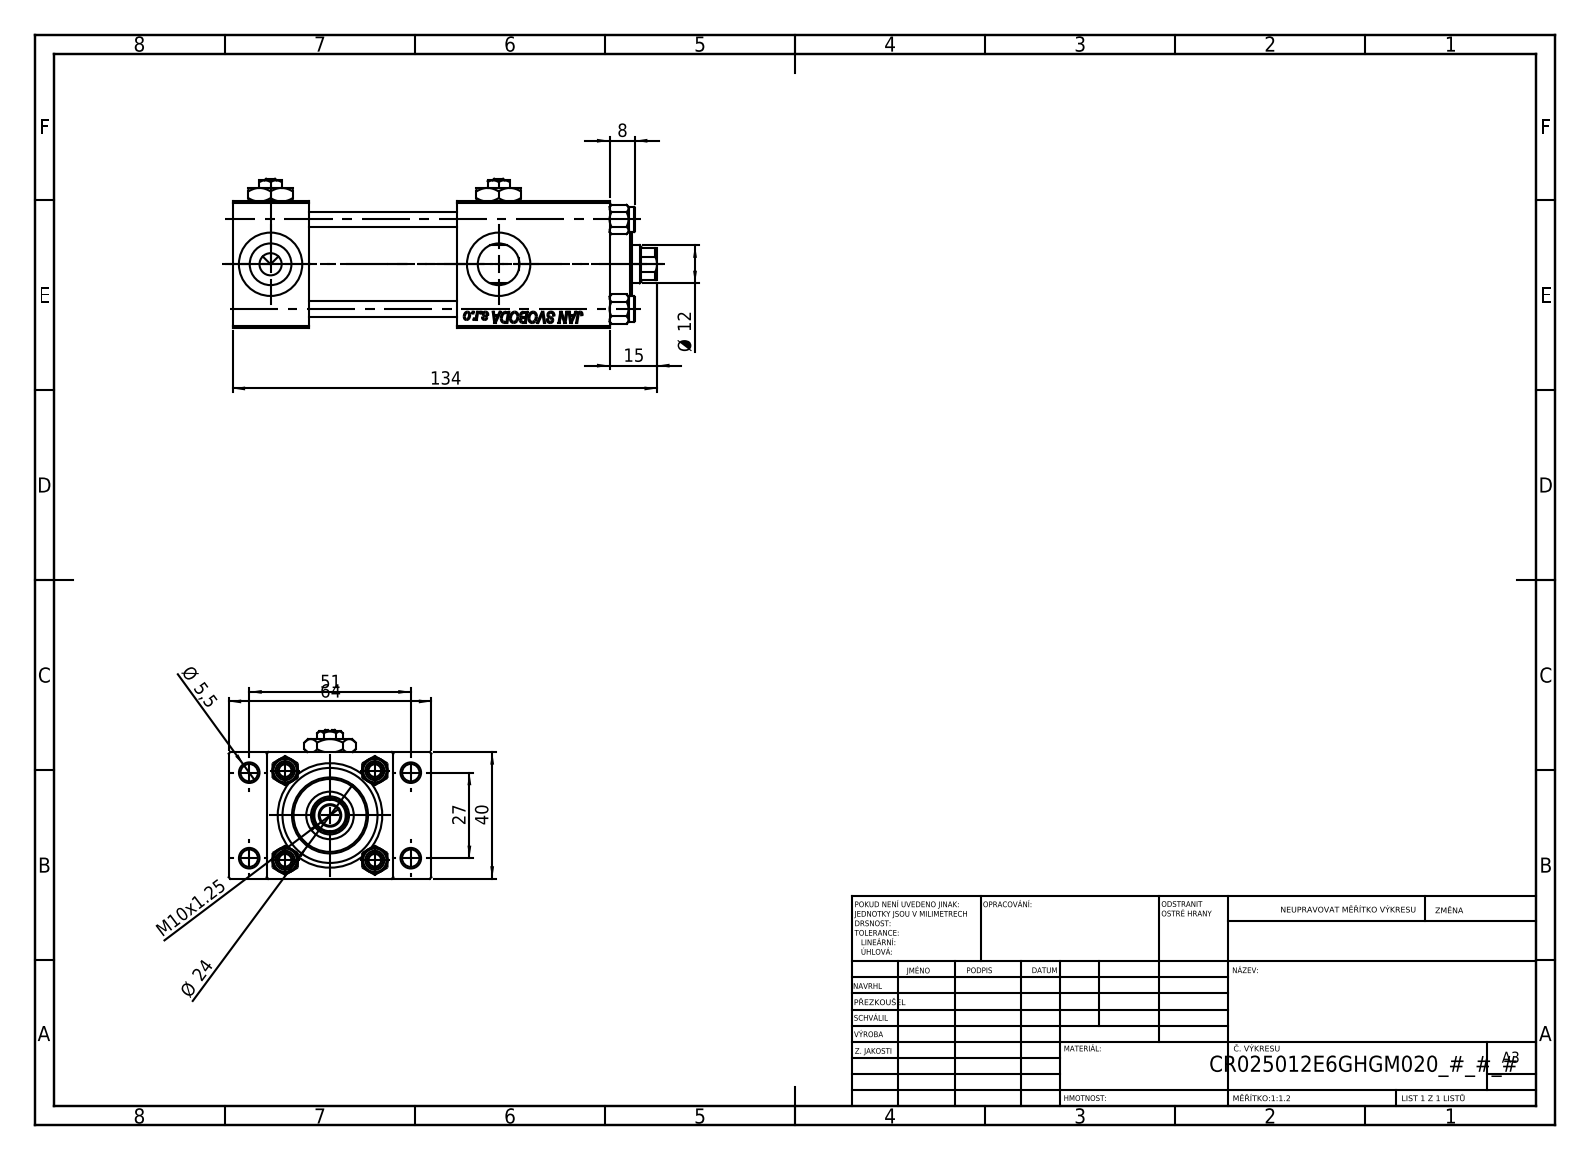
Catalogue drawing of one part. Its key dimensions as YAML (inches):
part_name: "V215CR_VCP_E; V215CR_E_Body; V215_VC_A; NUT_M5_E (+2 more)"
step_written_by: "SolidWorks 2019 (CONFIG_CONTROL_DESIGN)"
units: inches
bodies: {solids: 13, faces: 1235, planar: 544, cylindrical: 97, other: 594}
overall_size: [5.276, 2.52, 1.85]
volume: 9.874
surface_area: 99.5
round_holes:
  - {diameter: 0.787, count: 5}
  - {diameter: 0.197, count: 4}
  - {diameter: 0.217, count: 4}
  - {diameter: 0.518, count: 4}
  - {diameter: 0.276, count: 3}
  - {diameter: 0.256, count: 1}
  - {diameter: 0.472, count: 1}
  - {diameter: 0.591, count: 1}
  - {diameter: 0.984, count: 1}
  - {diameter: 1.181, count: 1}
round_bosses_or_shafts:
  - {diameter: 0.315, count: 4}
  - {diameter: 1.22, count: 1}
  - {diameter: 0.945, count: 1}
partial_cylinders:
  - {radius: 0.217, count: 1}
face_to_face_distances: [1.575, 0.945, 0.472, 2.047, 4.685, 3.74, 3.555, 2.61, 1.13, 1.85]
hole_center_spacings: [0.448, 0.788, 1.114, 1.136, 1.177, 1.561, 1.903, 1.063]
